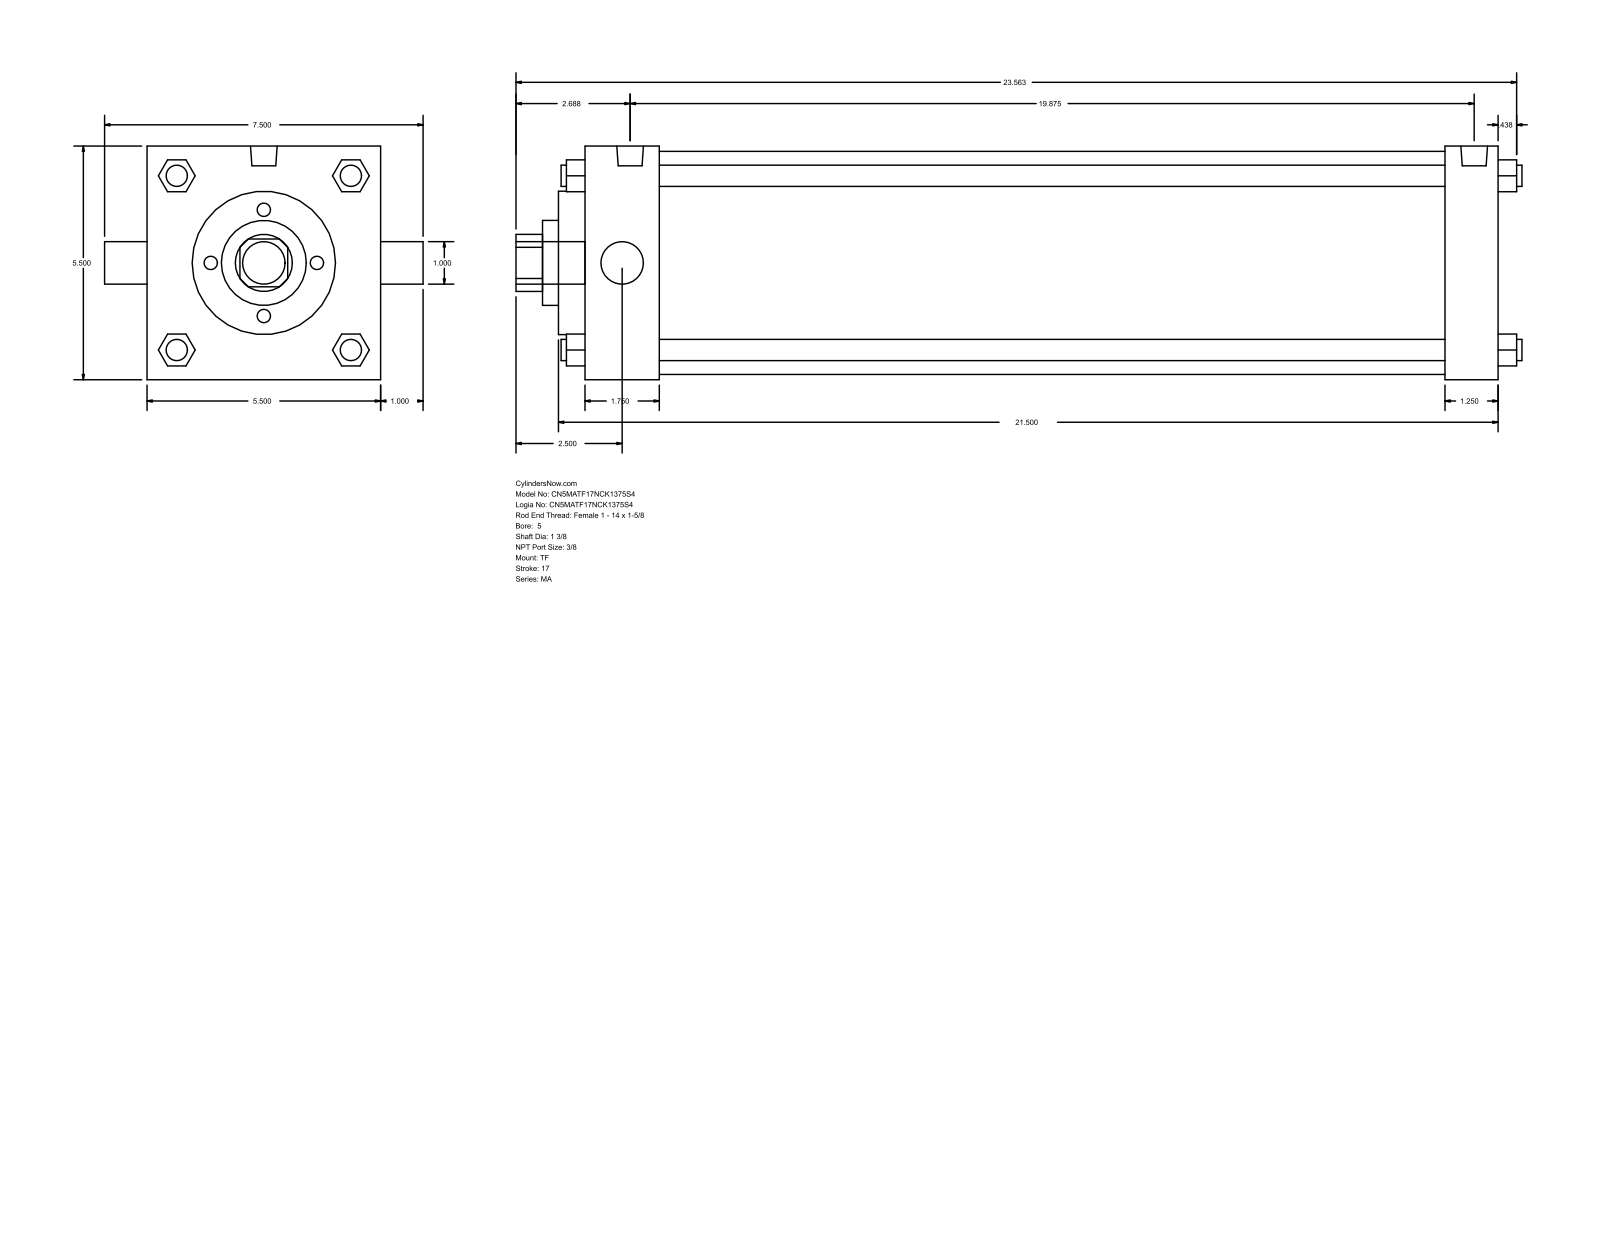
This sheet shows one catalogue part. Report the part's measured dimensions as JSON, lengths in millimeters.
{"part_name": "MA_TF__0500_1.375", "step_written_by": "GSSL Pune (CONFIG_CONTROL_DESIGN)", "units": "millimeters", "bodies": {"solids": 0, "faces": 122, "planar": 93, "cylindrical": 29, "other": 0}, "overall_size": [601.66, 190.5, 139.7], "round_holes": [[25.4, 1], [34.92, 1], [50.8, 1], [85.72, 1], [133.35, 1]], "round_bosses_or_shafts": [[12.7, 4], [11.11, 3], [15.93, 2], [25.4, 1]], "partial_cylinders_radius": [[17.06, 1]], "face_to_face_distances": [139.7, 546.11, 514.35, 31.76, 44.45, 469.9, 501.66, 15.87, 60.32, 530.22]}
